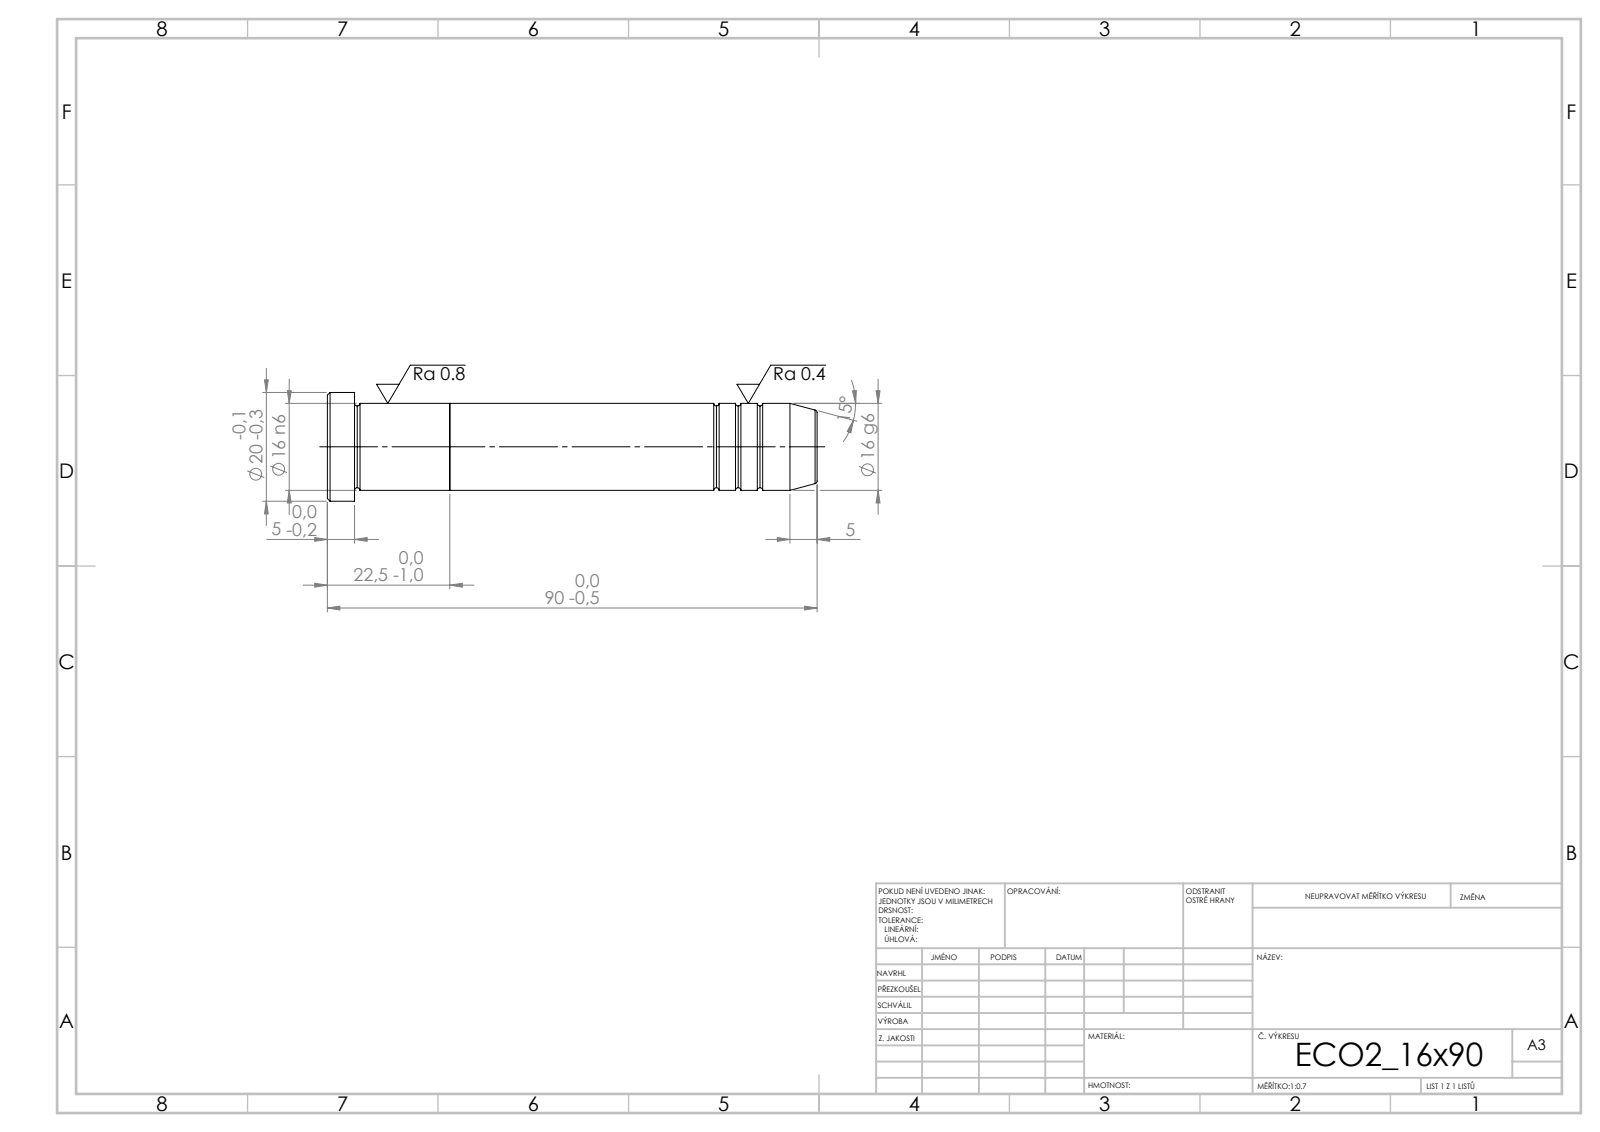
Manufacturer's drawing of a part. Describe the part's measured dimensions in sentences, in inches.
Its 3-D file was written by "SolidWorks 2019 (CONFIG_CONTROL_DESIGN)". It is 2 solids with 39 faces: 5 planar, 12 cylindrical and 22 other. Overall it measures 3.543 by 0.787 by 0.787 inches. Its volume is 1.124 cubic inches and its surface area 8.713 square inches. Round bosses or shafts: 1 of diameter 0.787, 1 of diameter 0.63. The main face-to-face distances are 0.886, 2.657, 3.543, 3.346, 0.689, 0.197.
